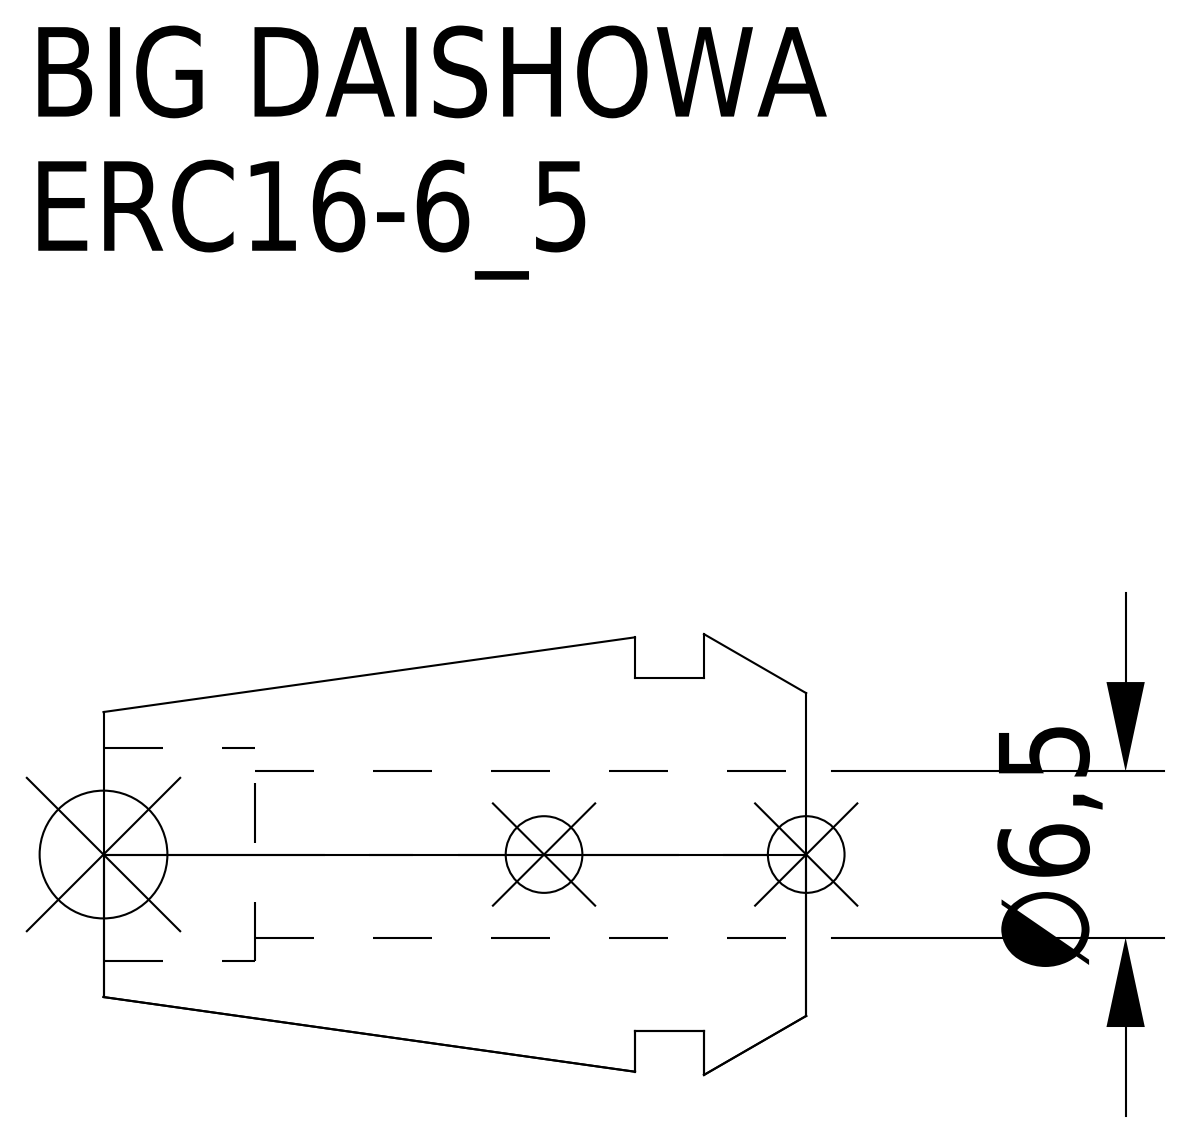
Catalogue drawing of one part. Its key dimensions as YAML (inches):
part_name: "ERC16-6_5"
step_written_by: "CREO PARAMETRIC BY PTC INC, 2016380 (AUTOMOTIVE_DESIGN)"
units: inches
bodies: {solids: 1, faces: 15, planar: 5, cylindrical: 6, other: 4}
overall_size: [1.083, 0.679, 0.679]
volume: 0.205
surface_area: 3.373
round_holes:
  - {diameter: 0.256, count: 1}
  - {diameter: 0.327, count: 1}
round_bosses_or_shafts:
  - {diameter: 0.543, count: 1}
face_to_face_distances: [0.157, 0.264, 0.106, 1.083, 0.925, 0.819, 0.85, 0.692, 0.586, 0.233]
